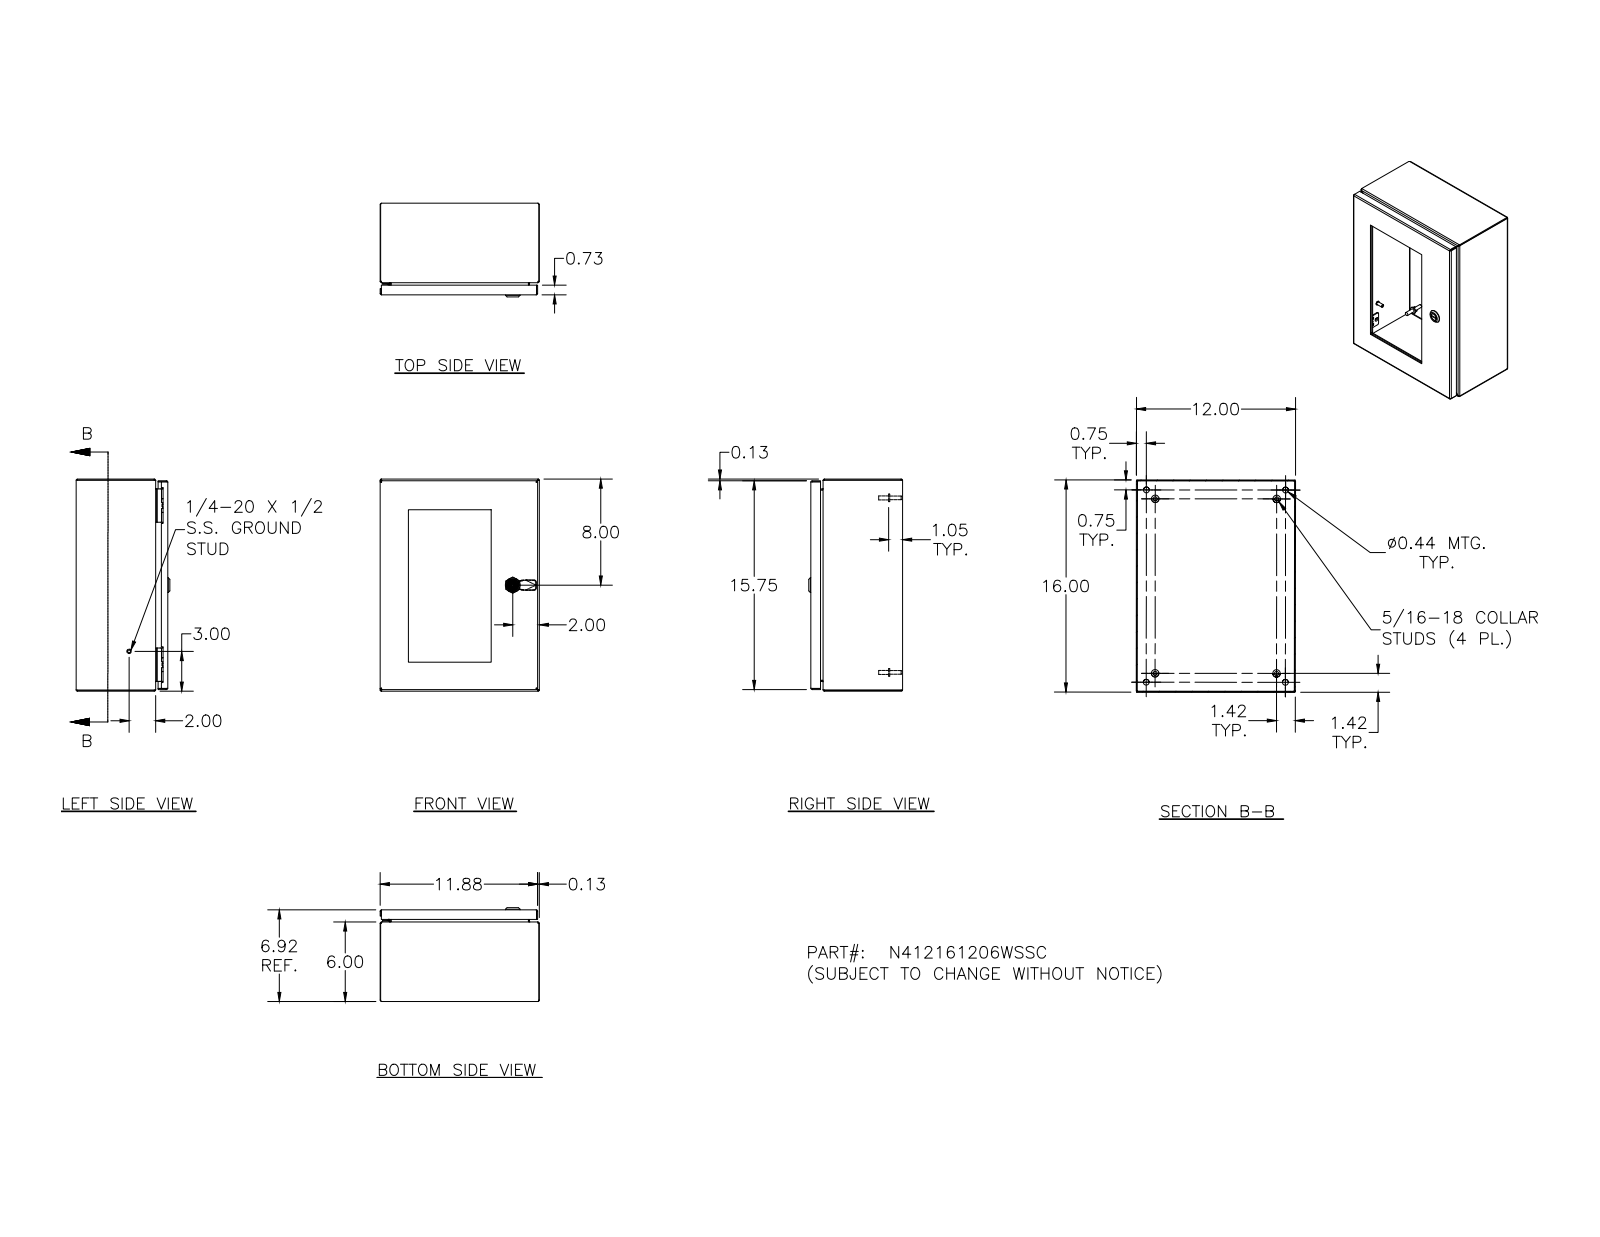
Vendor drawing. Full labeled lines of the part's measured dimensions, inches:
Part name (STEP PRODUCT): N412161206WSSC; N412161206WSSCBKP; N4121612WSSCLID; HFW328176 (+8 more)
STEP written by: Autodesk Inventor 2011 (AUTOMOTIVE_DESIGN)
Units: inches
Bodies: 58 solids, 1748 faces (688 planar, 541 cylindrical, 519 other)
Overall size (bounding box): 16 × 12 × 7.075
Volume: 82.96 in³ · Surface area: 1 846 in²
Round holes (diameter × count): ⌀0.156 ×12, ⌀0.281 ×10, ⌀0.093 ×4, ⌀0.152 ×4, ⌀0.167 ×4, ⌀0.172 ×4, ⌀0.188 ×4, ⌀0.437 ×4, ⌀0.187 ×1, ⌀0.197 ×1, ⌀0.315 ×1, ⌀0.394 ×1
Round bosses / shafts (diameter × count): ⌀0.25 ×10, ⌀0.19 ×10, ⌀0.253 ×9, ⌀0.563 ×4, ⌀0.36 ×4, ⌀0.32 ×4, ⌀0.3 ×4, ⌀0.275 ×4
Partial cylindrical surfaces — rounded edges, fillets, slot ends (radius × count): R0.031 ×34, R0.05 ×26, R0.105 ×24, R0.016 ×18, R0.125 ×16, R0.02 ×9, R0.032 ×8, R0.157 ×4
Main face-to-face distances: 0.074, 6.843, 6.769, 11.926, 15.926, 6.917, 11.852, 12, 0.25, 6.593
Hole centre spacings: 4, 12, 6.221, 8.5, 8.585, 11.862, 7.5, 0.5
